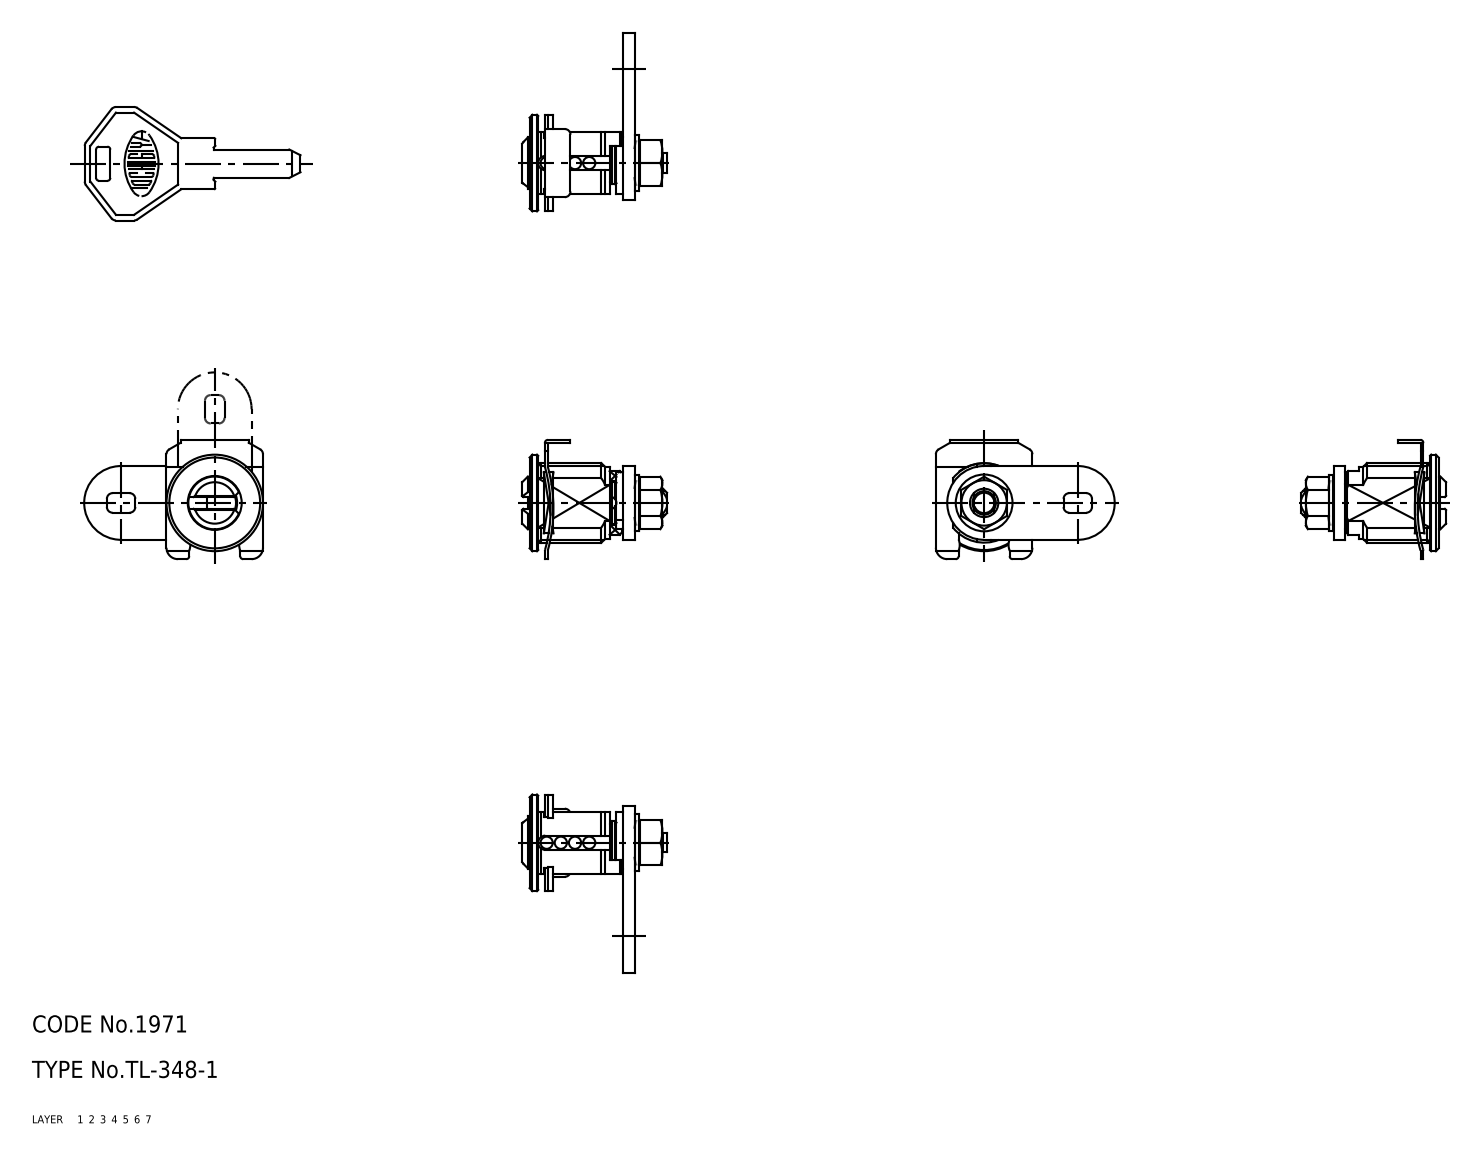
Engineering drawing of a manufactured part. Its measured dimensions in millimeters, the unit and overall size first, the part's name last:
Units: millimetres
Overall size (bounding box): 87.57 × 33.12 × 21
Volume: 3 788 mm³ · Surface area: 4 519 mm²
Bodies: 7 solids, 218 faces (0 planar, 0 cylindrical, 218 other)
Part name (STEP PRODUCT): washer; retainer; nut_A; lock (+4 more)
STEP written by: CADfix (AUTOMOTIVE_DESIGN)
